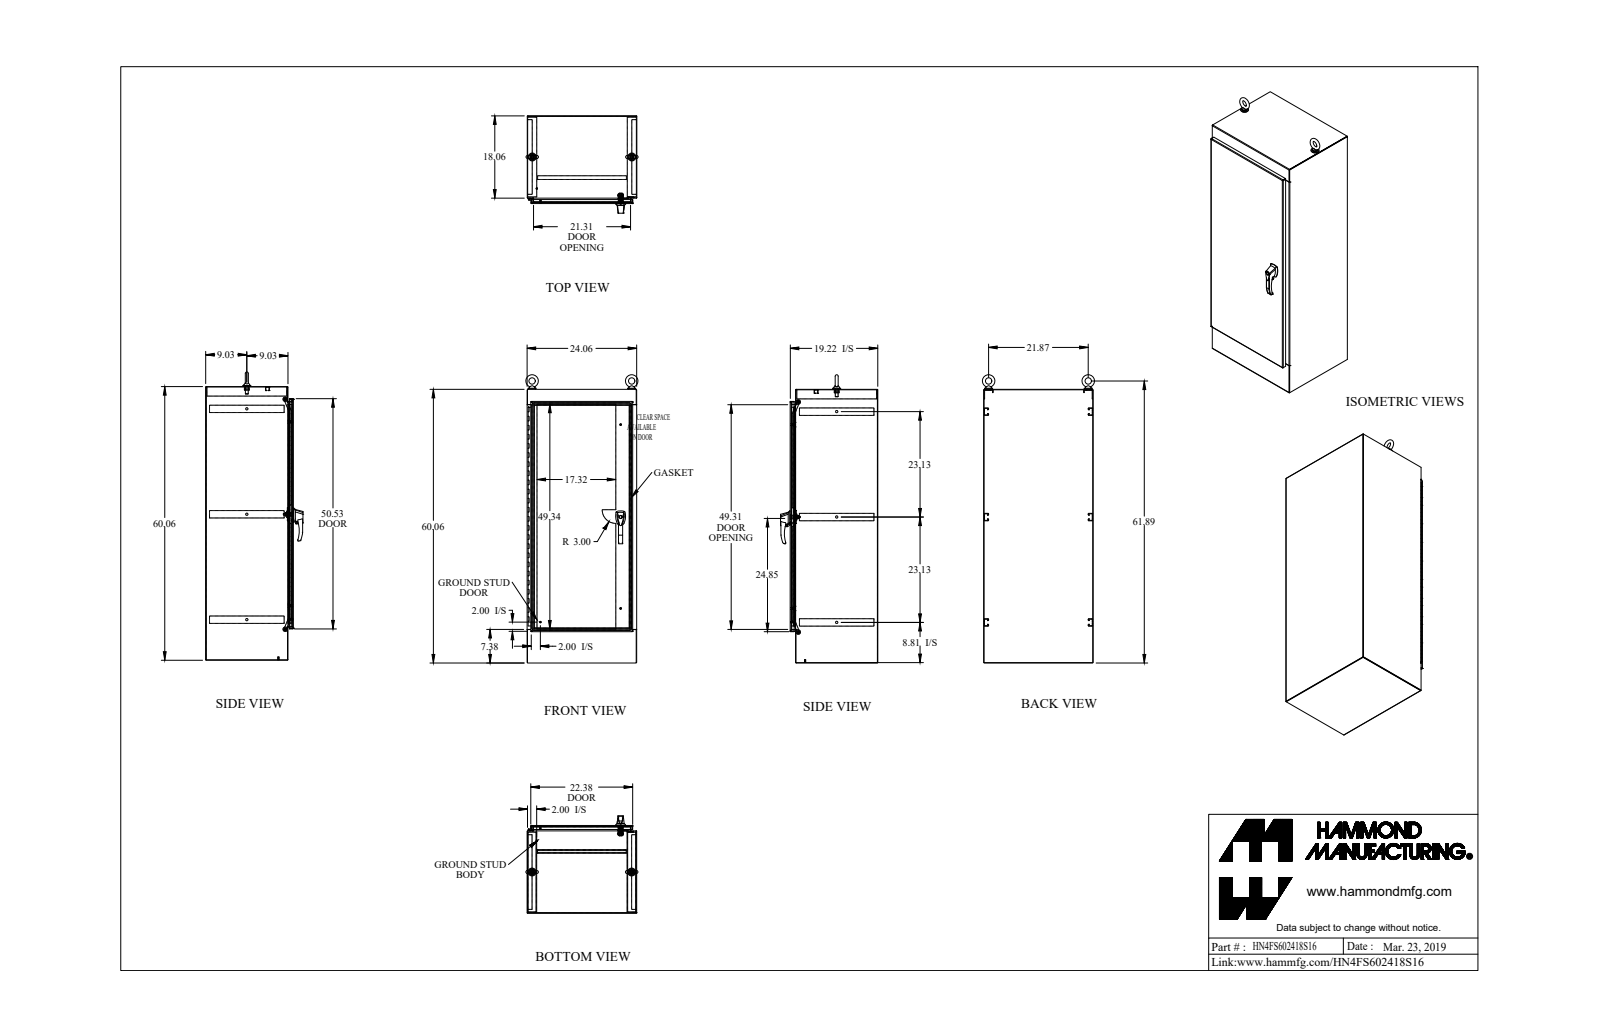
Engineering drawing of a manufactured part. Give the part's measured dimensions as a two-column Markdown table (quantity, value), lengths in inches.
| quantity | value |
| --- | --- |
| part name | HN4FS602418S16 |
| STEP written by | SolidWorks 2018 (AUTOMOTIVE_DESIGN) |
| units | inches |
| bodies | 56 solids, 1763 faces (820 planar, 778 cylindrical, 165 other) |
| overall size | 63.256 × 24.604 × 21.362 |
| volume | 717.2 in³ |
| surface area | 14 994 in² |
| round holes (diameter × count) | 0.304 × 8, 0.35 × 7, 0.5 × 3, 0.25 × 2, 0.257 × 2, 0.28 × 2, 0.281 × 2, 0.313 × 2, 0.39 × 2, 0.413 × 2, 0.527 × 2, 0.68 × 2 |
| round bosses / shafts (diameter × count) | 1.75 × 2, 1.5 × 2, 1.25 × 2, 1 × 2, 0.75 × 2, 0.738 × 2, 0.63 × 2, 0.625 × 2 |
| partial cylindrical surfaces (radius × count) | 0.043 × 42, 0.138 × 36, 0.5 × 23, 0.125 × 22, 0.017 × 16, 0.06 × 15, 0.048 × 13, 0.143 × 13 |
| main face-to-face distances | 0.095, 19.152, 23.965, 23.87, 19.057, 19.247, 24.06, 59.965, 17.965, 1.187 |
| hole center spacings | 6, 12, 18, 24, 30, 1.126, 1.287, 7.433 |
